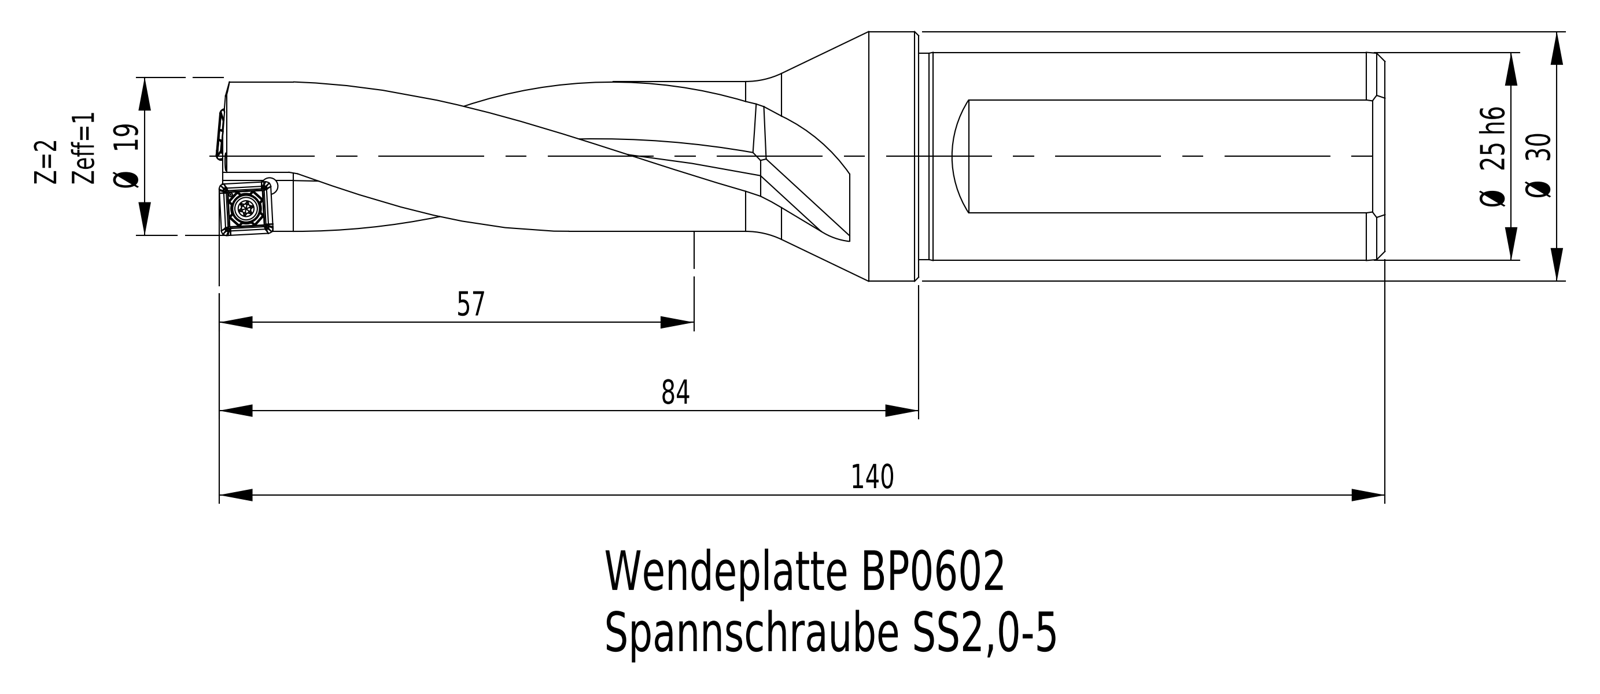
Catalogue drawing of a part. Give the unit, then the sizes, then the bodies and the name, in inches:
Units: inches
Overall size (bounding box): 5.496 × 1.181 × 1.181
Round holes (diameter × count): ⌀0.157 ×1, ⌀0.256 ×1
Round bosses / shafts (diameter × count): ⌀1.181 ×1, ⌀0.984 ×1, ⌀0.976 ×1, ⌀0.748 ×1, ⌀0.709 ×1
Main face-to-face distances: 5.496, 3.291, 2.205, 0.197, 3.094, 5.299, 1.35
Volume: 3.115 in³ · Surface area: 18.63 in²
Bodies: 1 solid, 45 faces (7 planar, 14 cylindrical, 24 other)
Part name (STEP PRODUCT): BW-19-57-25-06
STEP written by: SolidWorks 2015 (AUTOMOTIVE_DESIGN)
